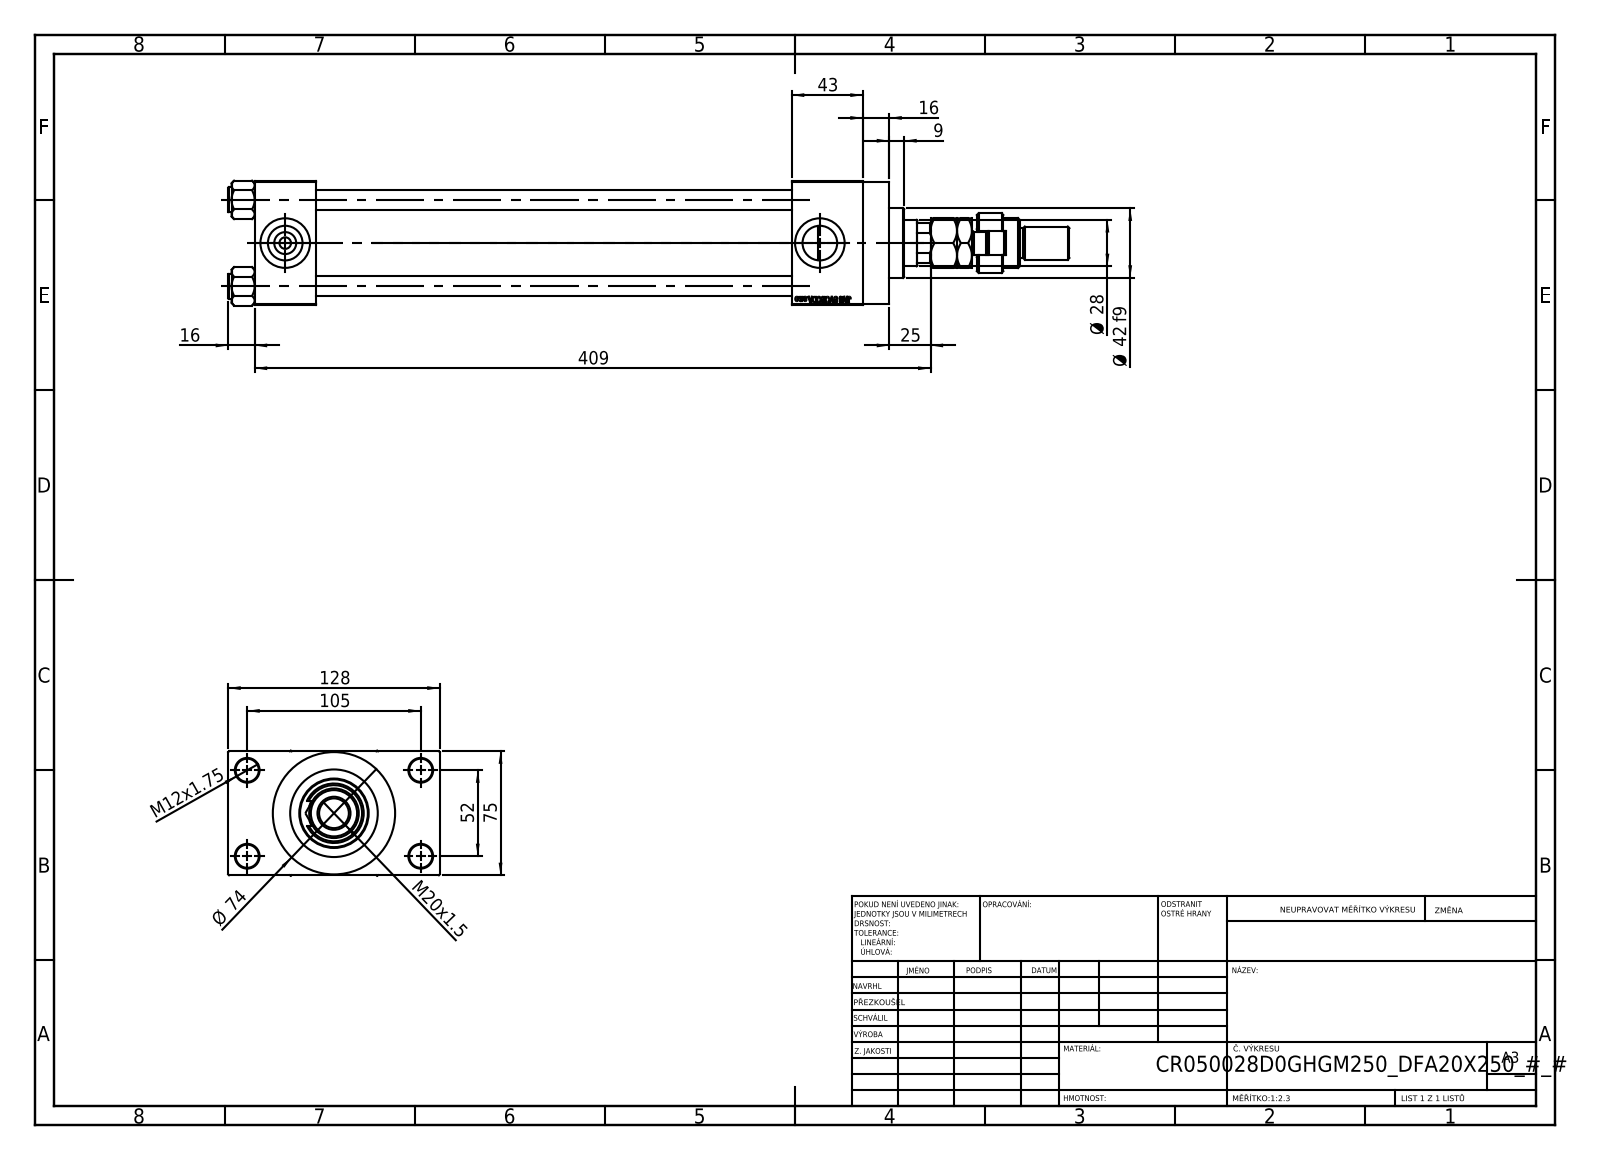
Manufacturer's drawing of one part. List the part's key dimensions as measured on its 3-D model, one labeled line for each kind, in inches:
Part name (STEP PRODUCT): V215_VC_A; V215CR_VCP_D; V215CR_D_Body; FEMALE_PART_FOR_DFA (+3 more)
STEP written by: SolidWorks 2019 (CONFIG_CONTROL_DESIGN)
Units: inches
Bodies: 13 solids, 1188 faces (525 planar, 101 cylindrical, 562 other)
Overall size (bounding box): 20.039 × 5.039 × 2.974
Volume: 74.2 in³ · Surface area: 488.8 in²
Round holes (diameter × count): ⌀0.472 ×4, ⌀0.551 ×4, ⌀0.276 ×2, ⌀0.825 ×2, ⌀1.181 ×2, ⌀0.728 ×1, ⌀1.102 ×1, ⌀1.22 ×1, ⌀1.614 ×1, ⌀1.969 ×1, ⌀2.087 ×1
Round bosses / shafts (diameter × count): ⌀0.591 ×4, ⌀2.913 ×1, ⌀2.205 ×1, ⌀1.654 ×1, ⌀1.417 ×1, ⌀1.181 ×1, ⌀0.866 ×1, ⌀0.787 ×1
Partial cylindrical surfaces — rounded edges, fillets, slot ends (radius × count): R0.295 ×1, R0.472 ×1, R0.531 ×1
Main face-to-face distances: 2.953, 11.339, 1.457, 12.795, 1.043, 1.693, 14.488, 13.031, 3.996, 0.63
Hole centre spacings: 1.037, 1.456, 2.059, 2.3, 2.307, 3.096, 3.715, 2.047
